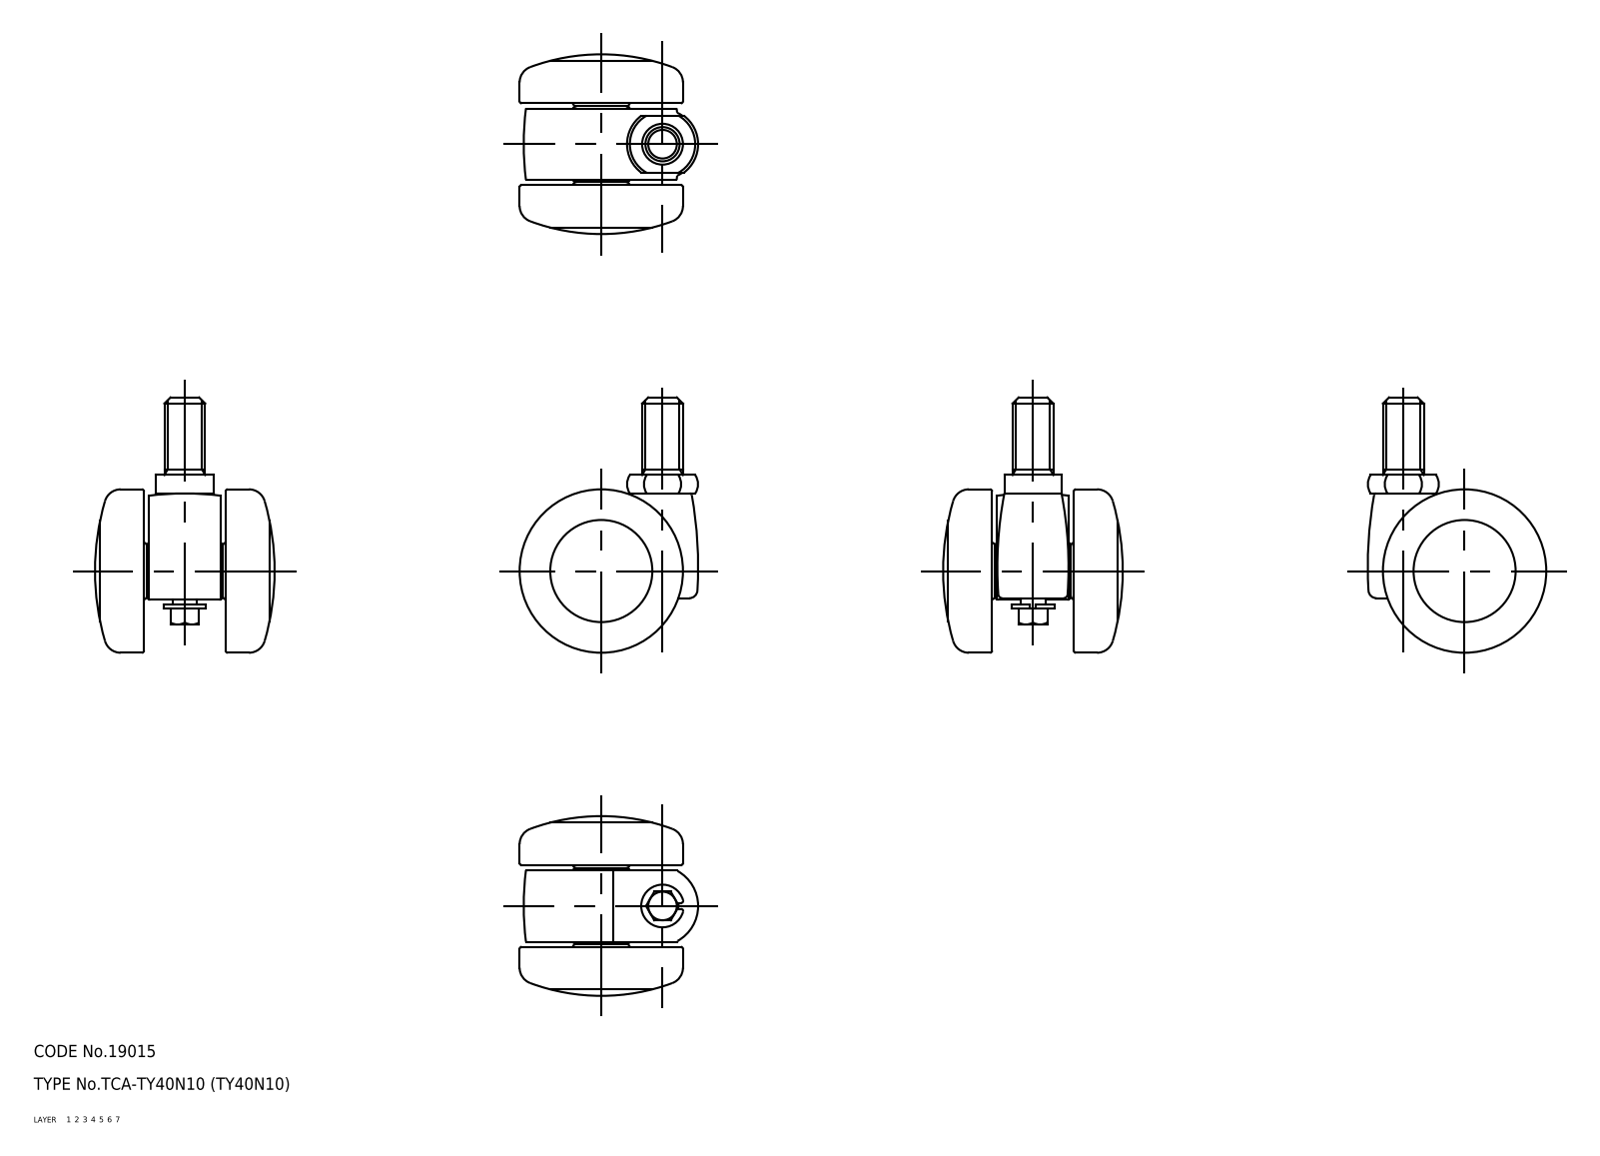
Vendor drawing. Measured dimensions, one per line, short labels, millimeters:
name: wheel; main shaft; TY40N10_10165_36
written by: CADfix (AUTOMOTIVE_DESIGN)
unit: mm
bodies: 4 solids, 117 faces (0 planar, 0 cylindrical, 117 other)
size: 62.5 × 44 × 43.72
volume: 39 425 mm³; area: 17 684 mm²
